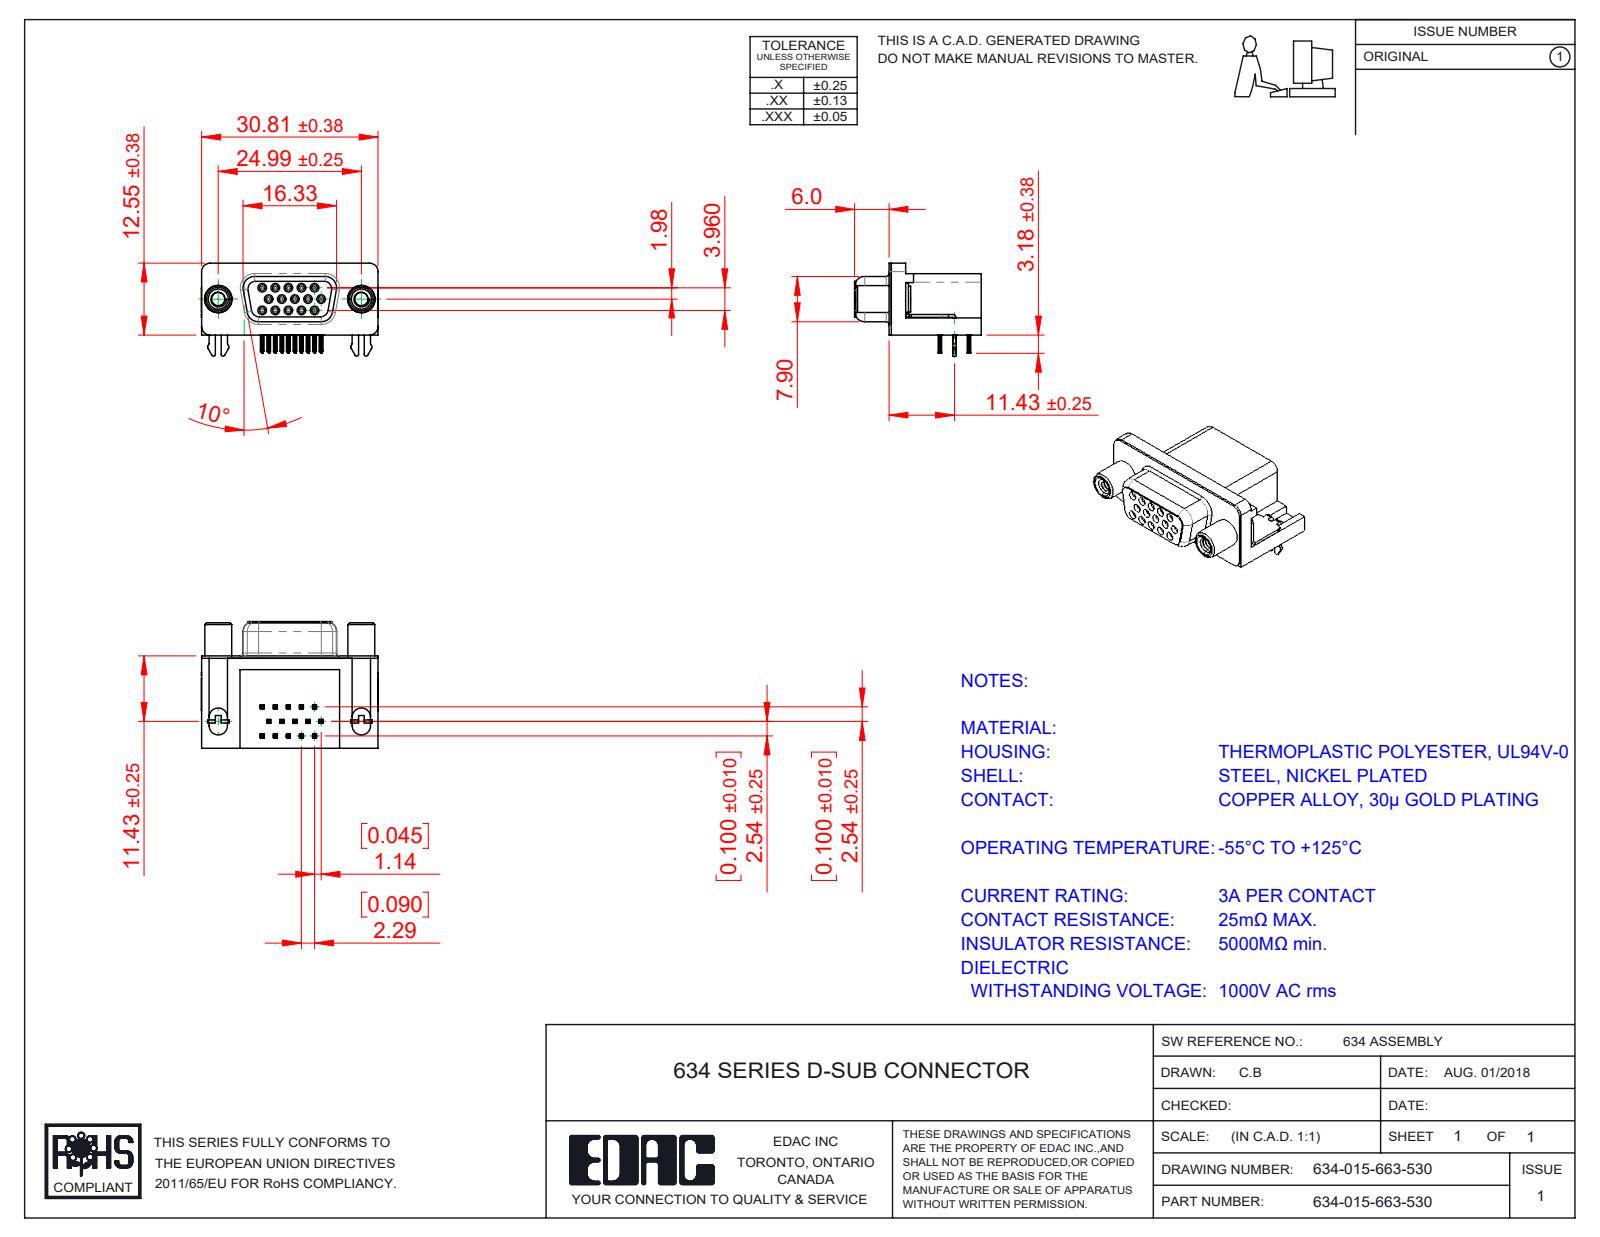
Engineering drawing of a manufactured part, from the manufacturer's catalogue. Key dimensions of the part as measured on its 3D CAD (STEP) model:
Part name (STEP PRODUCT): Contact Bottom; Contact Middle; 634 Housing; 2 Prong Board Lock (+4 more)
STEP written by: SolidWorks 2016 (CONFIG_CONTROL_DESIGN)
Units: millimetres
Bodies: 21 solids, 2455 faces (1090 planar, 615 cylindrical, 750 other)
Overall size (bounding box): 30.89 × 22.1 × 16.25
Volume: 4 643 mm³ · Surface area: 6 705 mm²
Round holes (diameter × count): ⌀0.8 ×15, ⌀0.9 ×15, ⌀2.3 ×2, ⌀3.1 ×2, ⌀4 ×2, ⌀4.8 ×2, ⌀5 ×2
Round bosses / shafts (diameter × count): ⌀1.2 ×15, ⌀4.9 ×2, ⌀4.7 ×2, ⌀4.5 ×2, ⌀3.85 ×2
Partial cylindrical surfaces — rounded edges, fillets, slot ends (radius × count): R0.1 ×120, R0.15 ×60, R0.35 ×30, R1 ×19, R0.34 ×15, R0.5 ×10, R1.35 ×8, R1.6 ×8
Main face-to-face distances: 0.4, 10.35, 15.7, 16.1, 0.35, 2.5, 2.9, 0.6, 10.7, 0.5
Hole centre spacings: 2.29, 2.28, 3.96, 4.57, 6.05, 3.97, 4.58, 6.86
